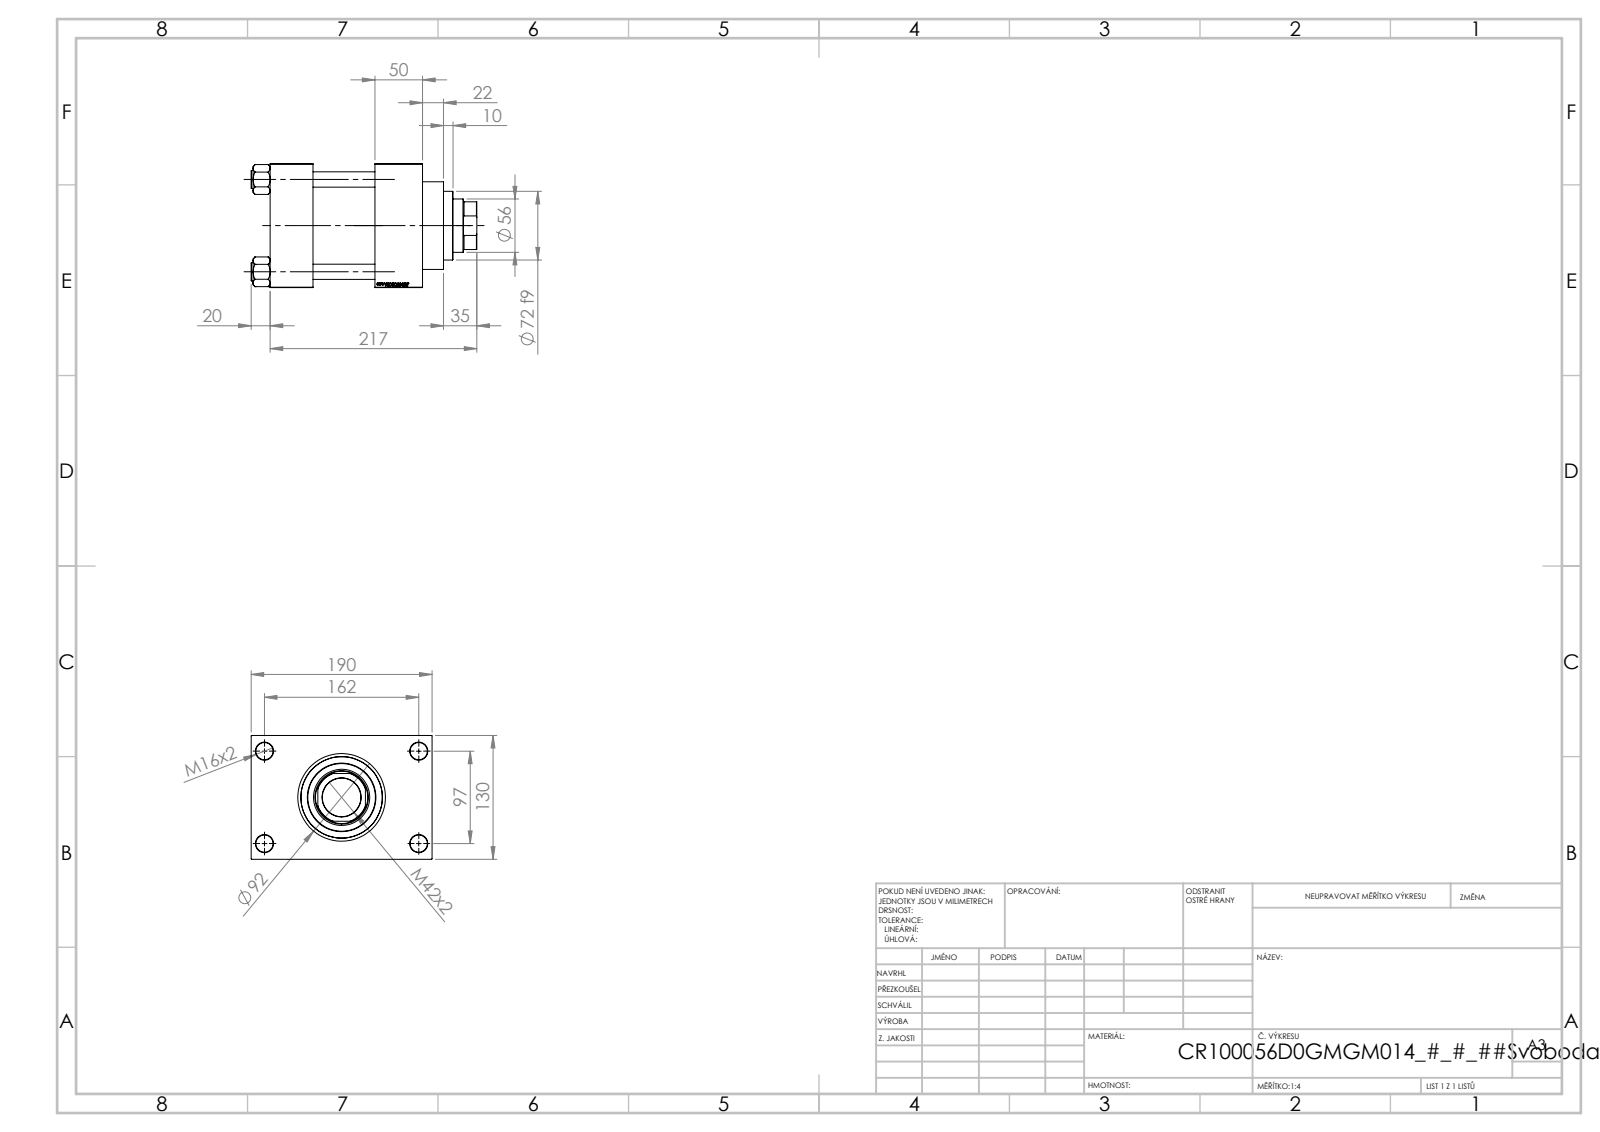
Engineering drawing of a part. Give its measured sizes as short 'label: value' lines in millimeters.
name: V215_VC_A; V215CR_VCP_D; V215CR_D_Body; NUT_M5_D (+1 more)
written by: SolidWorks 2019 (CONFIG_CONTROL_DESIGN)
unit: mm
bodies: 11 solids, 1151 faces (545 planar, 88 cylindrical, 518 other)
size: 237 × 190 × 130
volume: 2 603 000 mm³; area: 356 077 mm²
holes: 4× ⌀16, 4× ⌀18, 2× ⌀7, 2× ⌀26.44, 2× ⌀35, 1× ⌀40.5, 1× ⌀56, 1× ⌀59, 1× ⌀76, 1× ⌀85.5, 1× ⌀100
bosses: 4× ⌀19, 1× ⌀106, 1× ⌀92, 1× ⌀72
rounds: 1× R27
face distances: 160, 130, 65, 50, 45, 110, 115, 30, 96, 14
hole spacings: 32.55, 68.52, 94.41, 96.9, 102.27, 129.45, 161.73, 97
